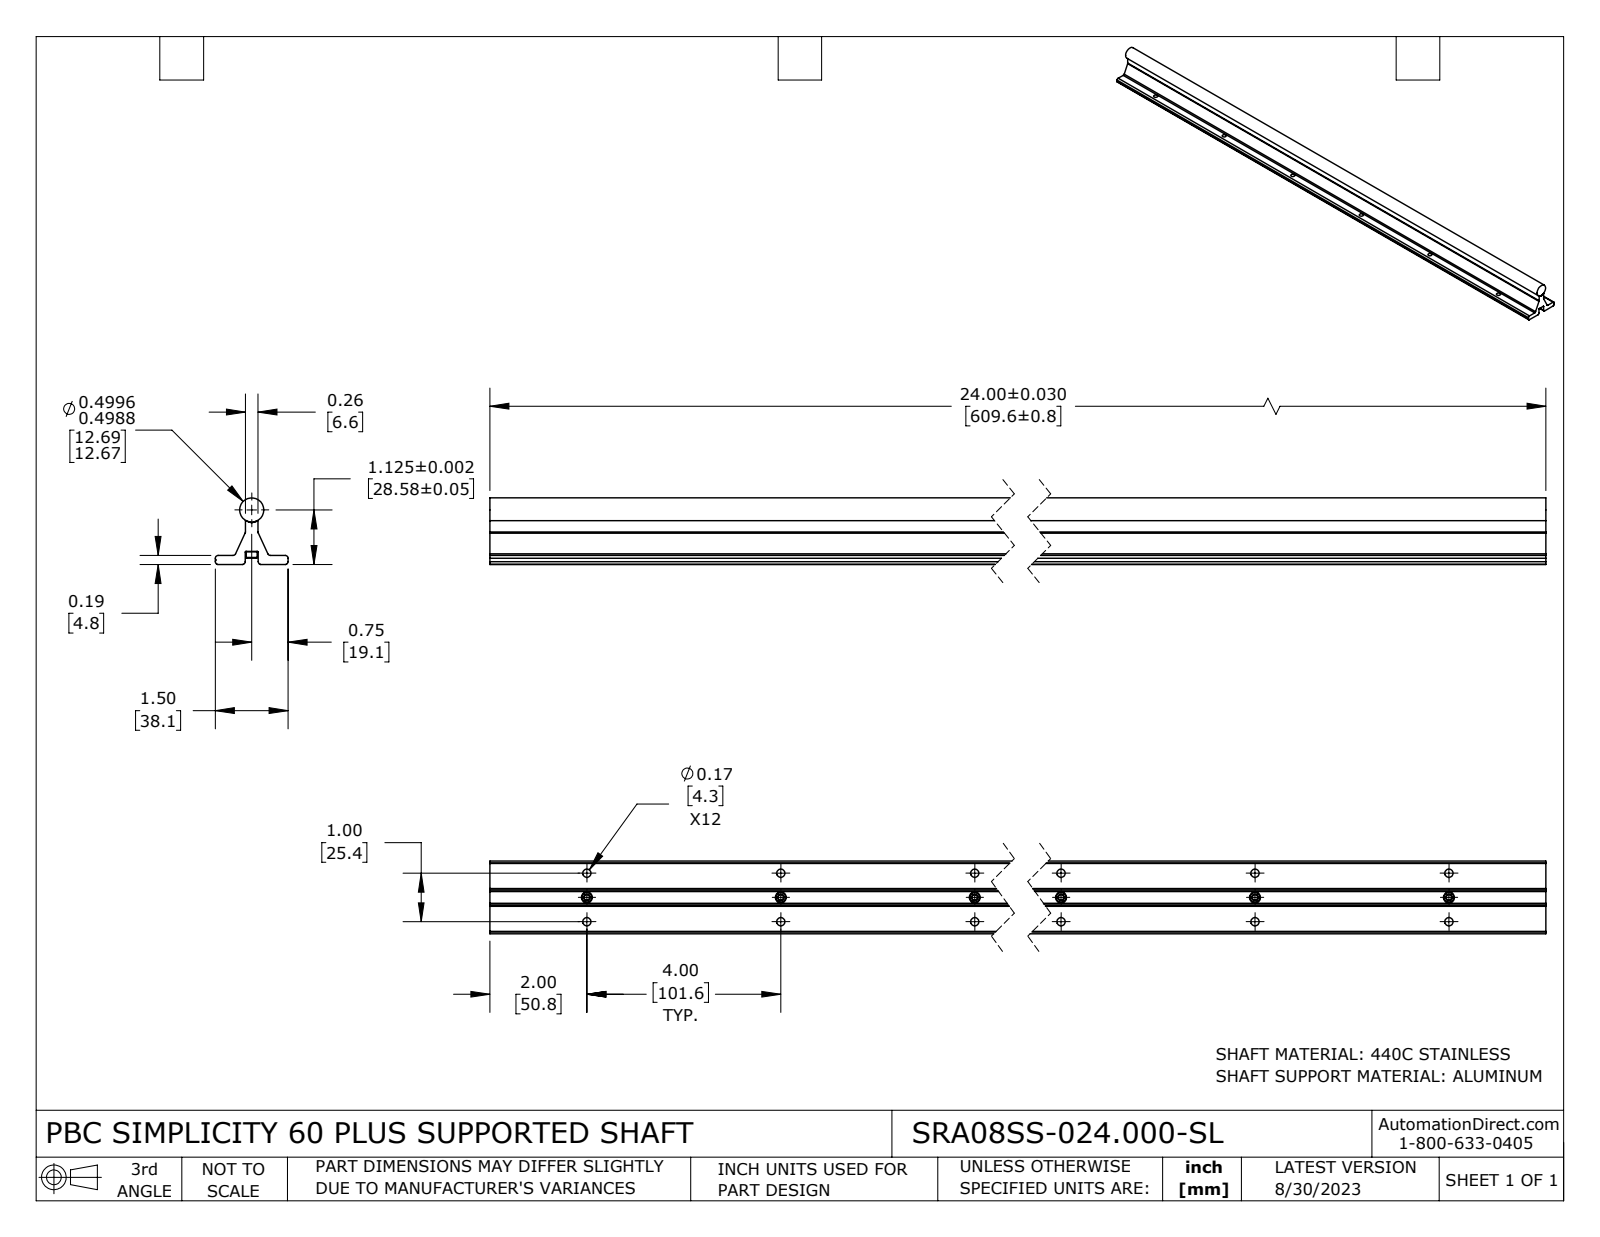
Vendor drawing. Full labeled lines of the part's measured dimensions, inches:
Part name (STEP PRODUCT): SRA08SS-024.000-SL
STEP written by: SolidWorks 2021 (CONFIG_CONTROL_DESIGN)
Units: inches
Bodies: 8 solids, 281 faces (93 planar, 98 cylindrical, 90 other)
Overall size (bounding box): 24 × 1.5 × 1.375
Volume: 16.38 in³ · Surface area: 162.3 in²
Round holes (diameter × count): ⌀0.17 ×18, ⌀0.116 ×6, ⌀0.156 ×6
Round bosses / shafts (diameter × count): ⌀0.226 ×6, ⌀0.138 ×6, ⌀0.5 ×1
Partial cylindrical surfaces — rounded edges, fillets, slot ends (radius × count): R0.06 ×8, R0.015 ×2, R0.062 ×1, R0.063 ×1
Main face-to-face distances: 0.187, 0.27, 0.265, 0.083, 0.26, 0.615, 0.62, 0.88, 0.885, 1.5
Hole centre spacings: 4.031, 8.016, 4, 0.5, 8, 12.01, 4.123, 12
